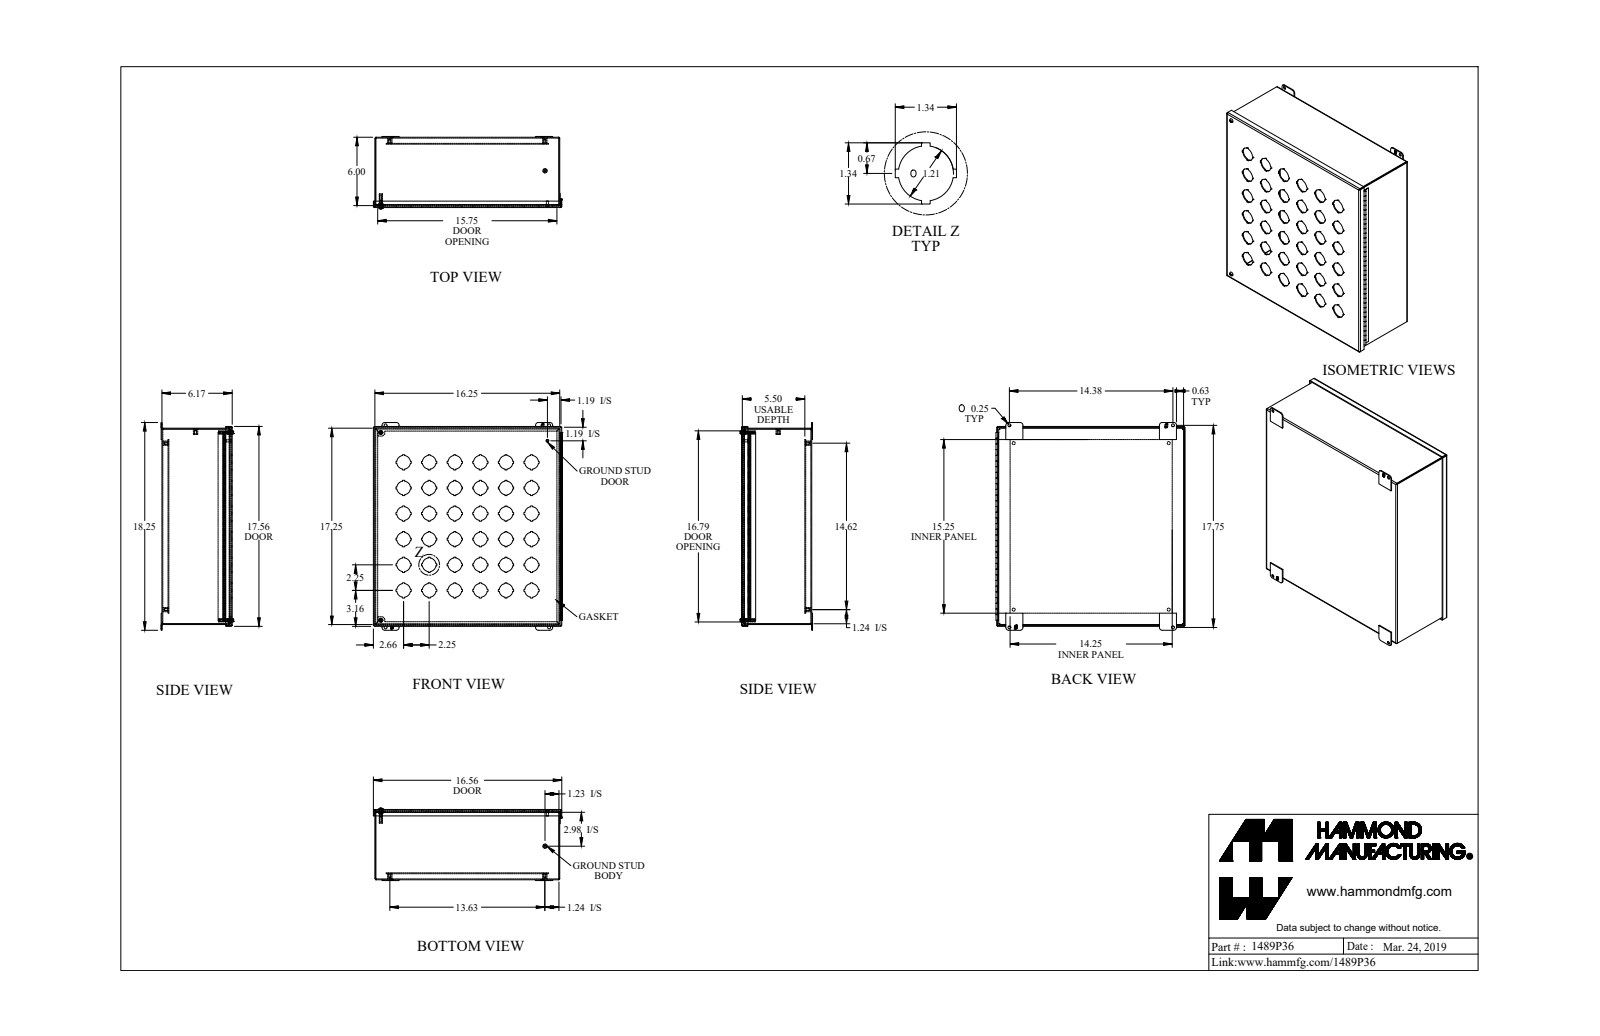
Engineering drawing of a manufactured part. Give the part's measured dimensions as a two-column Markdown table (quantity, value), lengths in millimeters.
| quantity | value |
| --- | --- |
| part name | 1489P36_Default |
| STEP written by | SolidWorks 2019 (CONFIG_CONTROL_DESIGN) |
| units | millimeters |
| bodies | 21 solids, 1373 faces (966 planar, 349 cylindrical, 58 other) |
| overall size | 463.6 × 422.2 × 161.8 |
| volume | 1 571 000 mm³ |
| surface area | 1 666 000 mm² |
| round holes (diameter × count) | 30.7 × 36, 6.4 × 6, 4 × 5, 6.7 × 4, 4 × 2, 10.3 × 2 |
| round bosses / shafts (diameter × count) | 9.5 × 5, 9.9 × 2, 7 × 2, 4.8 × 2, 3.8 × 2, 6.4 × 1, 4.8 × 1, 4.4 × 1 |
| partial cylindrical surfaces (radius × count) | 0.9 × 12, 2.7 × 12, 6.4 × 8, 4.1 × 2, 4.3 × 2 |
| main face-to-face distances | 1.8, 154.9, 141.4, 13.5, 153.1, 156.8, 15.3, 143.3, 11.7, 139.6 |
| hole center spacings | 127.8, 57.2, 80.8, 180.7, 114.3, 206.1, 171.5, 161.6 |
